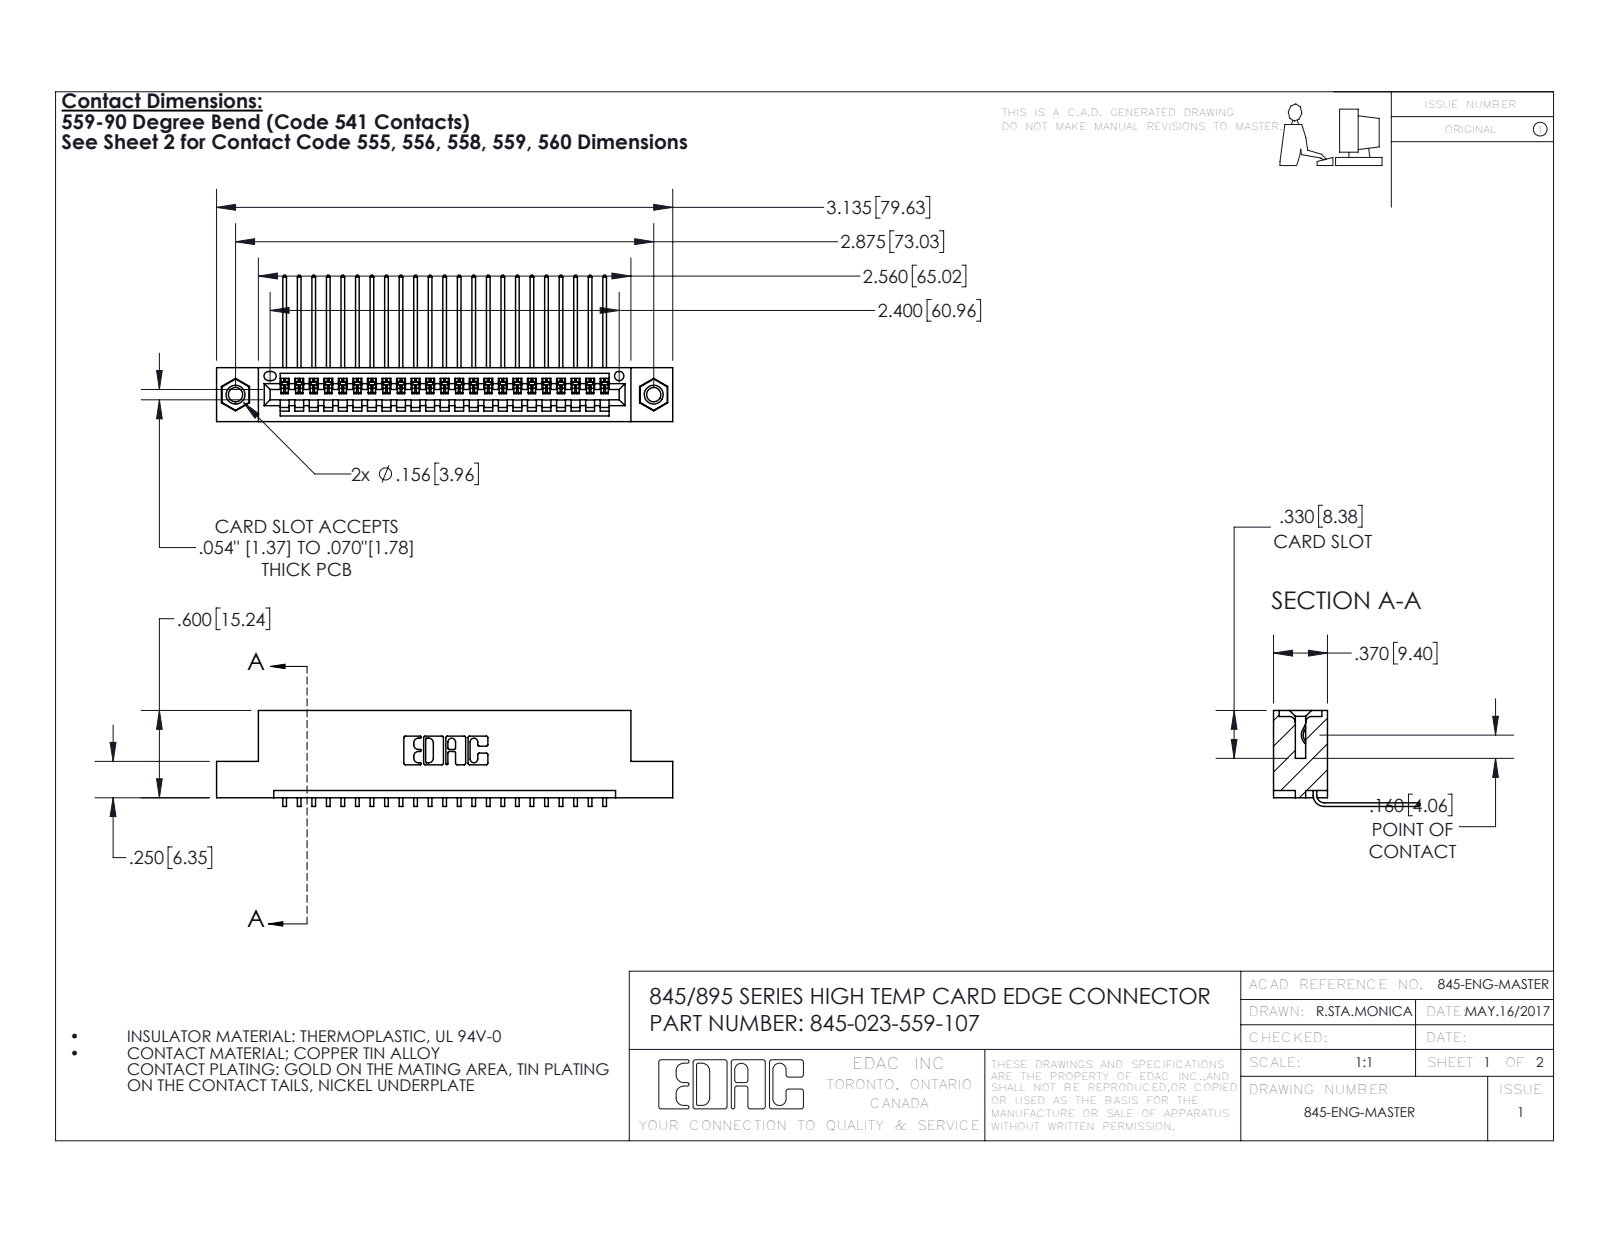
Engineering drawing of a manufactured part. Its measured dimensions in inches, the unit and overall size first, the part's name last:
Units: inches
Overall size (bounding box): 3.135 × 1.005 × 0.659
Round holes (diameter × count): ⌀0.098 ×2, ⌀0.125 ×2, ⌀0.156 ×2, ⌀0.064 ×1
Round bosses / shafts (diameter × count): ⌀0.155 ×2
Partial cylindrical surfaces — rounded edges, fillets, slot ends (radius × count): R0.006 ×46, R0.01 ×22, R0.007 ×6, R0.031 ×6, R0.026 ×3, R0.031 ×2, R0.04 ×2, R0.014 ×1
Main face-to-face distances: 0.072, 0.298, 0.37, 0.2, 0.098, 0.272, 0.025, 0.225, 0.149, 0.072
Hole centre spacings: 0.27, 2.641, 2.875
Volume: 0.456 in³ · Surface area: 15.74 in²
Bodies: 26 solids, 1566 faces (1078 planar, 472 cylindrical, 16 other)
Part name (STEP PRODUCT): 345 Part_Flush Mounting Lugs - 0.156 Dia-TI; 345-250-001_345-250-005-103; 345-292-001_558 559 Tail - 1; 345-023-559-107
STEP written by: SolidWorks 2016 (CONFIG_CONTROL_DESIGN)
